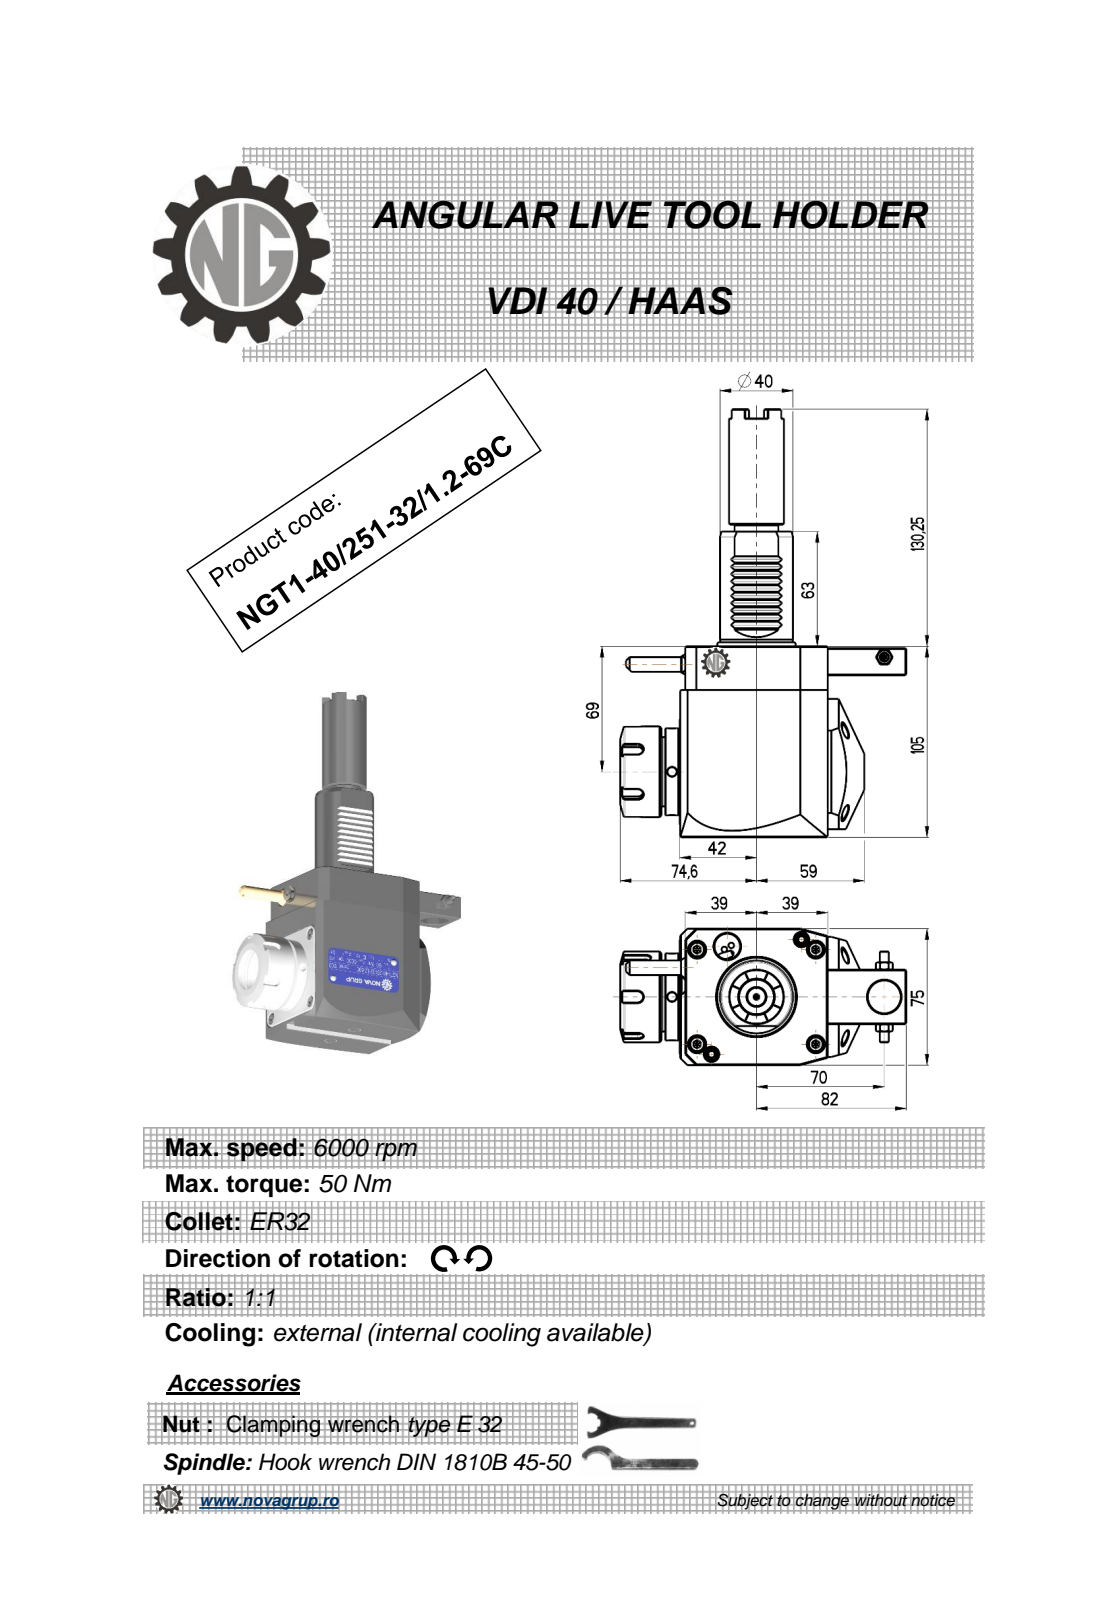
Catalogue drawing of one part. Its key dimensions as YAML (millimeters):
part_name: "NGT1_40_251_32_1_2_69C"
step_written_by: "PRO/ENGINEER BY PARAMETRIC TECHNOLOGY CORPORATION, 2010280 (CONFIG_CONTROL_DESIGN)"
units: millimeters
bodies: {solids: 1, faces: 459, planar: 226, cylindrical: 92, other: 141}
overall_size: [235.25, 156.6, 76.6]
volume: 860903
surface_area: 75807
round_holes:
  - {diameter: 5, count: 3}
  - {diameter: 3, count: 1}
  - {diameter: 4.2, count: 1}
  - {diameter: 9.5, count: 1}
  - {diameter: 18, count: 1}
  - {diameter: 19.5, count: 1}
  - {diameter: 27, count: 1}
round_bosses_or_shafts:
  - {diameter: 50, count: 1}
  - {diameter: 48, count: 1}
  - {diameter: 41, count: 1}
  - {diameter: 40, count: 1}
  - {diameter: 30, count: 1}
  - {diameter: 24, count: 1}
  - {diameter: 10, count: 1}
  - {diameter: 8.96, count: 1}
partial_cylinders:
  - {radius: 0.26, count: 12}
  - {radius: 0.3, count: 10}
  - {radius: 0.2, count: 6}
  - {radius: 3, count: 5}
  - {radius: 0.5, count: 1}
  - {radius: 40, count: 1}
face_to_face_distances: [75, 105, 81, 80.8, 1, 22.5, 3, 89, 2.8, 78]
hole_center_spacings: [16.19, 46.25, 61.13, 61.5, 70, 116.25, 132.22]
